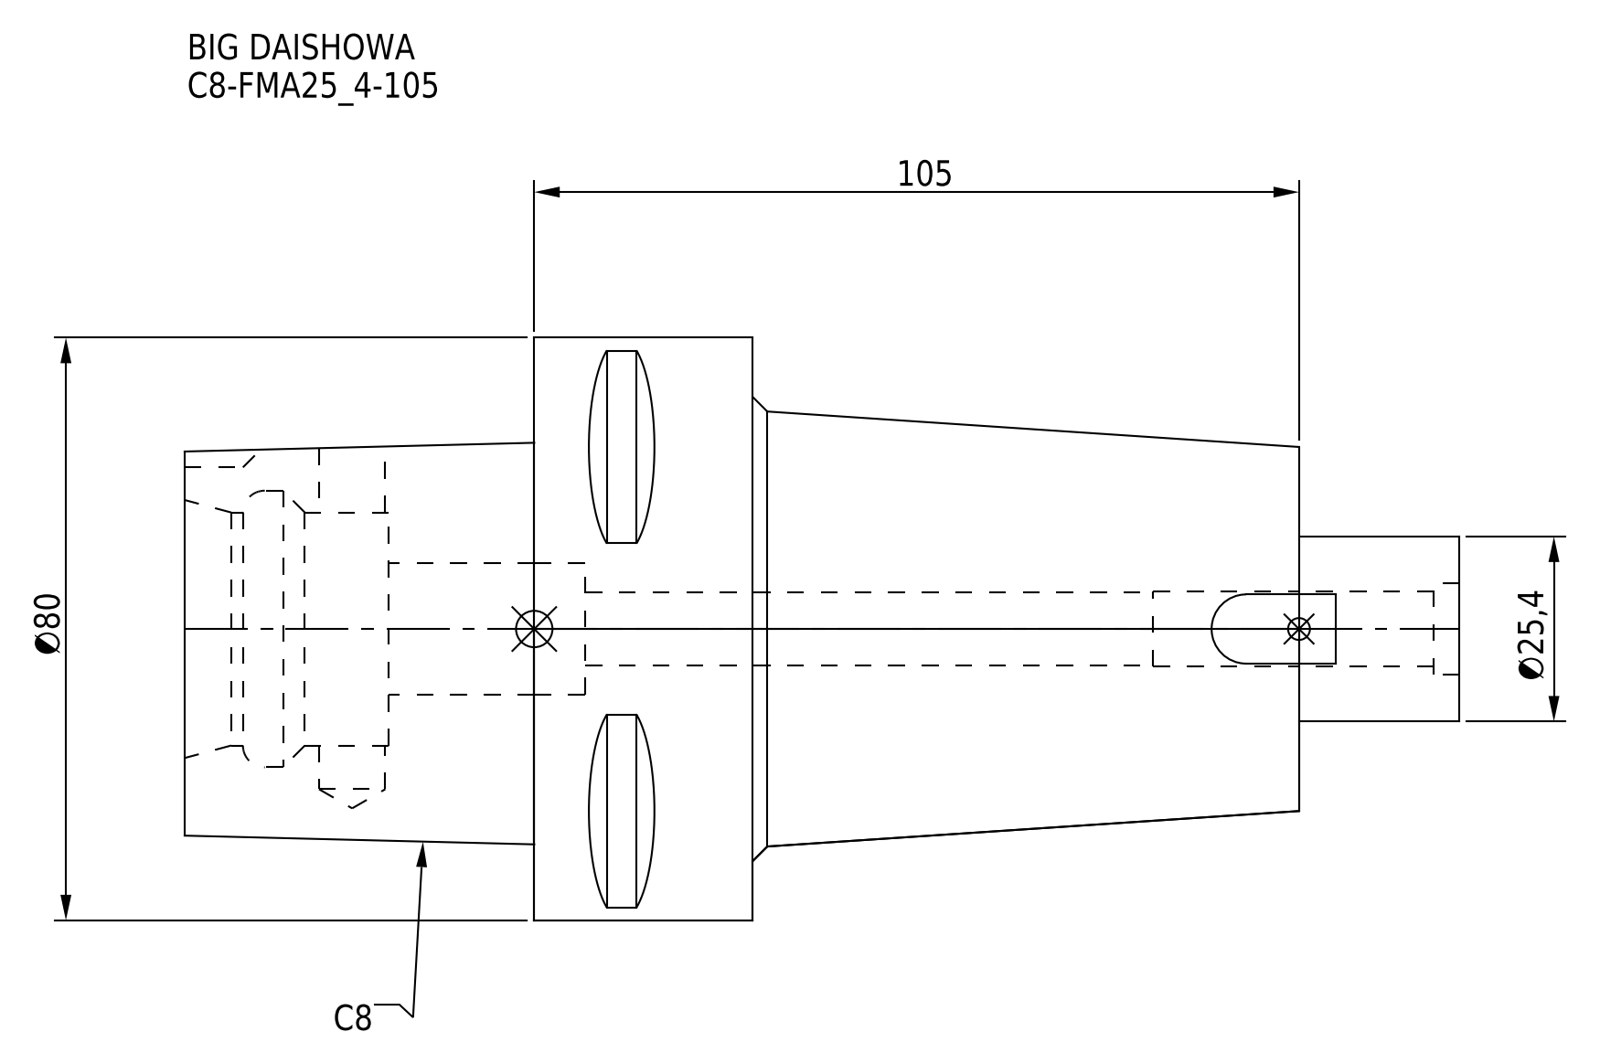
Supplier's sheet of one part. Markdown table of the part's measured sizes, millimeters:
| quantity | value |
| --- | --- |
| part name | C8-FMA25_4-105 |
| STEP written by | CREO PARAMETRIC BY PTC INC, 2016380 (AUTOMOTIVE_DESIGN) |
| units | millimeters |
| bodies | 1 solid, 78 faces (41 planar, 23 cylindrical, 14 other) |
| overall size | 175 × 80 × 80 |
| volume | 404 682 mm³ |
| surface area | 48 810 mm² |
| round holes (diameter × count) | 9.1 × 1, 10 × 1, 10.25 × 1, 12.5 × 1, 18 × 1, 32 × 1, 38 × 1 |
| round bosses / shafts (diameter × count) | 80 × 1, 25.4 × 1 |
| partial cylindrical surfaces (radius × count) | 6 × 1 |
| main face-to-face distances | 30, 105, 75, 48, 78, 153, 20, 125, 50, 28 |
